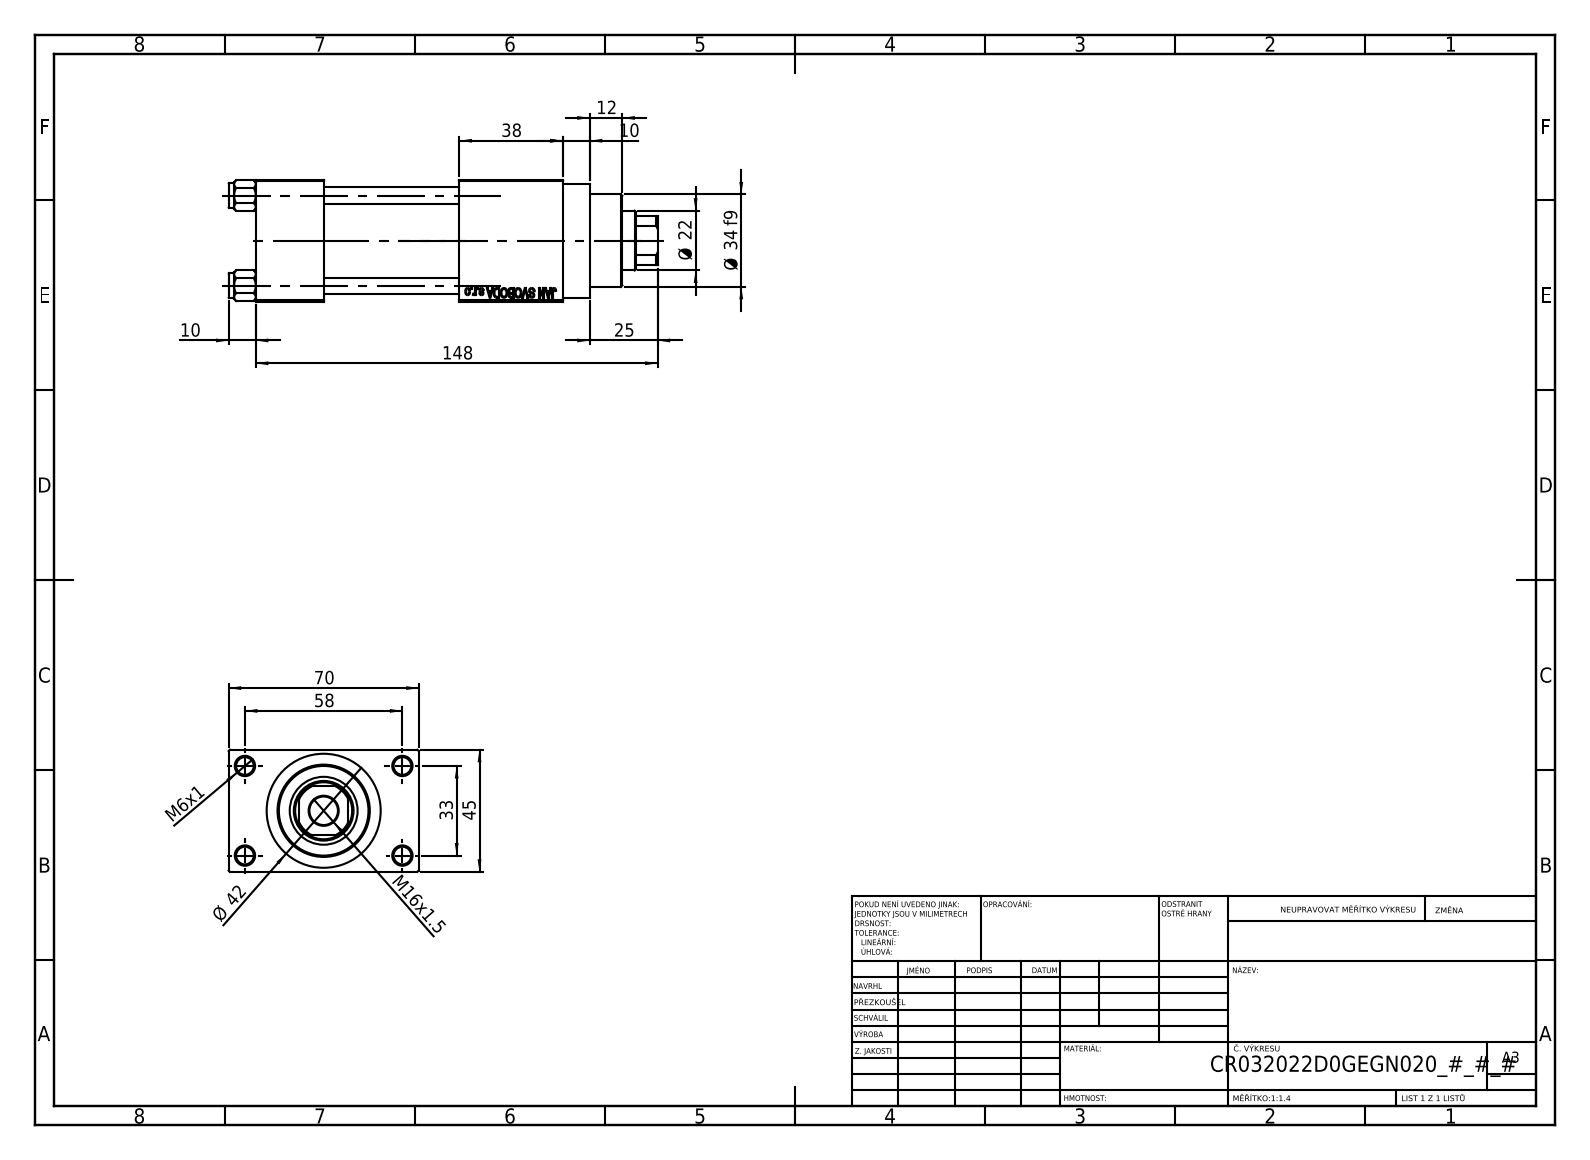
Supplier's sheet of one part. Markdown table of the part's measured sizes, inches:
| quantity | value |
| --- | --- |
| part name | V215_VC_A; V215CR_D_Body; V215CR_D_TYCINKA; NUT_M5_D (+1 more) |
| STEP written by | SolidWorks 2019 (CONFIG_CONTROL_DESIGN) |
| units | inches |
| bodies | 11 solids, 1103 faces (496 planar, 89 cylindrical, 518 other) |
| overall size | 6.22 × 2.756 × 1.772 |
| volume | 14.93 in³ |
| surface area | 123.2 in² |
| round holes (diameter × count) | 0.236 × 4, 0.256 × 4, 0.276 × 2, 0.518 × 2, 0.787 × 2, 0.413 × 1, 0.866 × 1, 0.945 × 1, 0.984 × 1, 1.26 × 1, 1.299 × 1 |
| round bosses / shafts (diameter × count) | 0.354 × 4, 1.654 × 1, 1.496 × 1, 1.339 × 1 |
| partial cylindrical surfaces (radius × count) | 0.413 × 1 |
| main face-to-face distances | 1.772, 0.984, 0.492, 2.264, 1.969, 2.953, 3.465, 2.756, 1.496, 4.449 |
| hole center spacings | 0.488, 0.924, 1.307, 1.314, 1.392, 1.795, 2.219, 1.299 |
